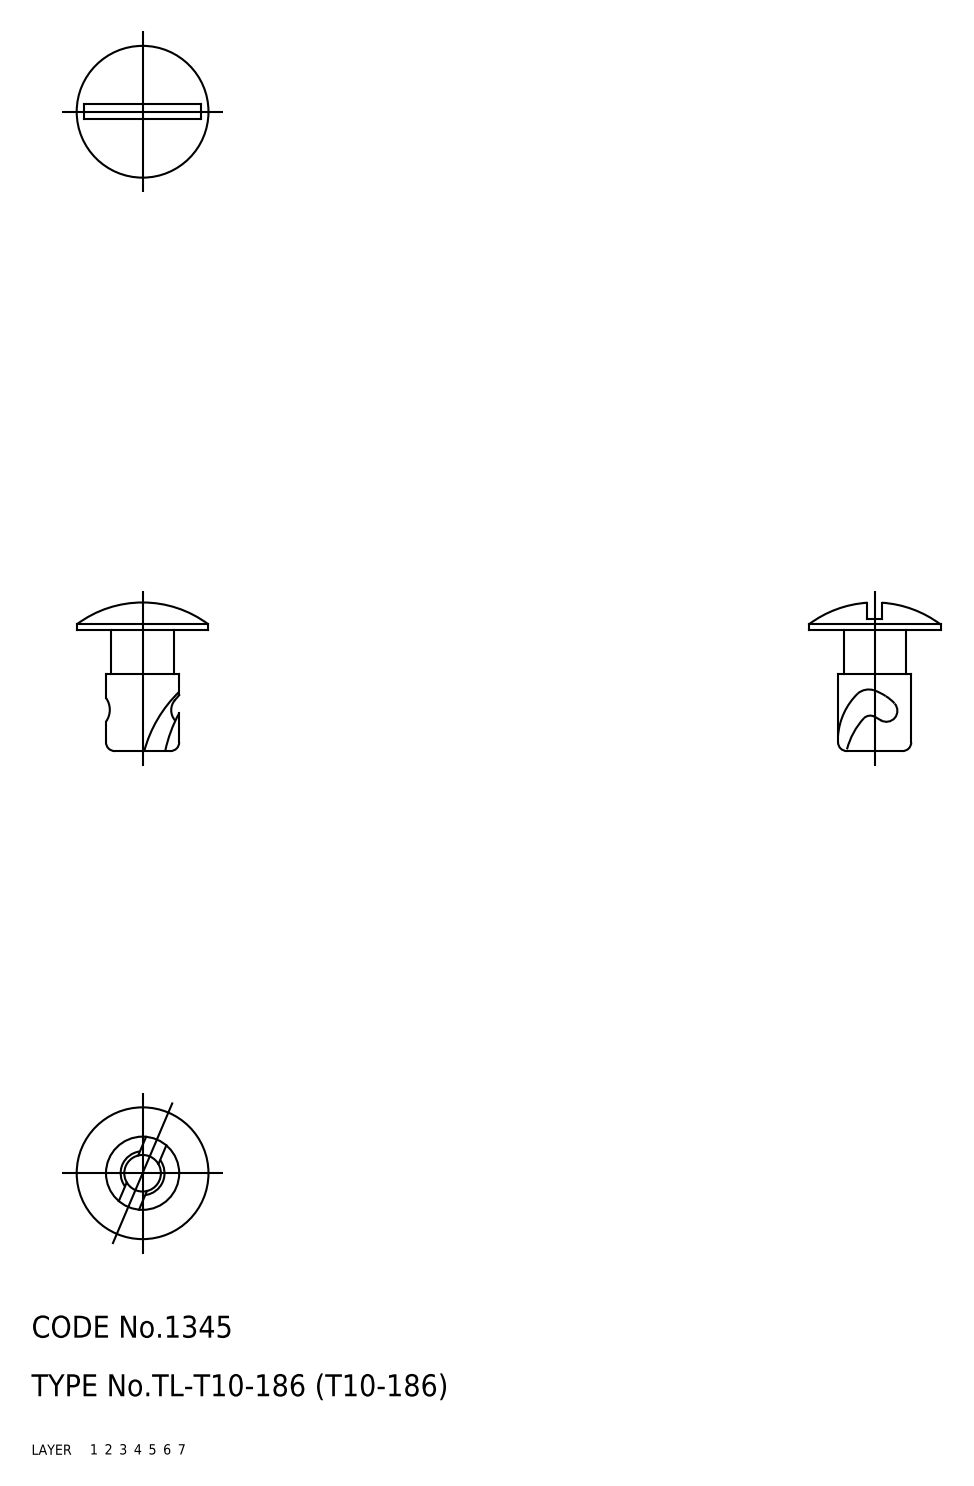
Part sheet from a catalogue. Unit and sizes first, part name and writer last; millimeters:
Units: millimetres
Overall size (bounding box): 20.27 × 18 × 18
Volume: 1 368 mm³ · Surface area: 1 278 mm²
Bodies: 1 solid, 36 faces (0 planar, 0 cylindrical, 36 other)
Part name (STEP PRODUCT): fastener
STEP written by: CADfix (AUTOMOTIVE_DESIGN)
